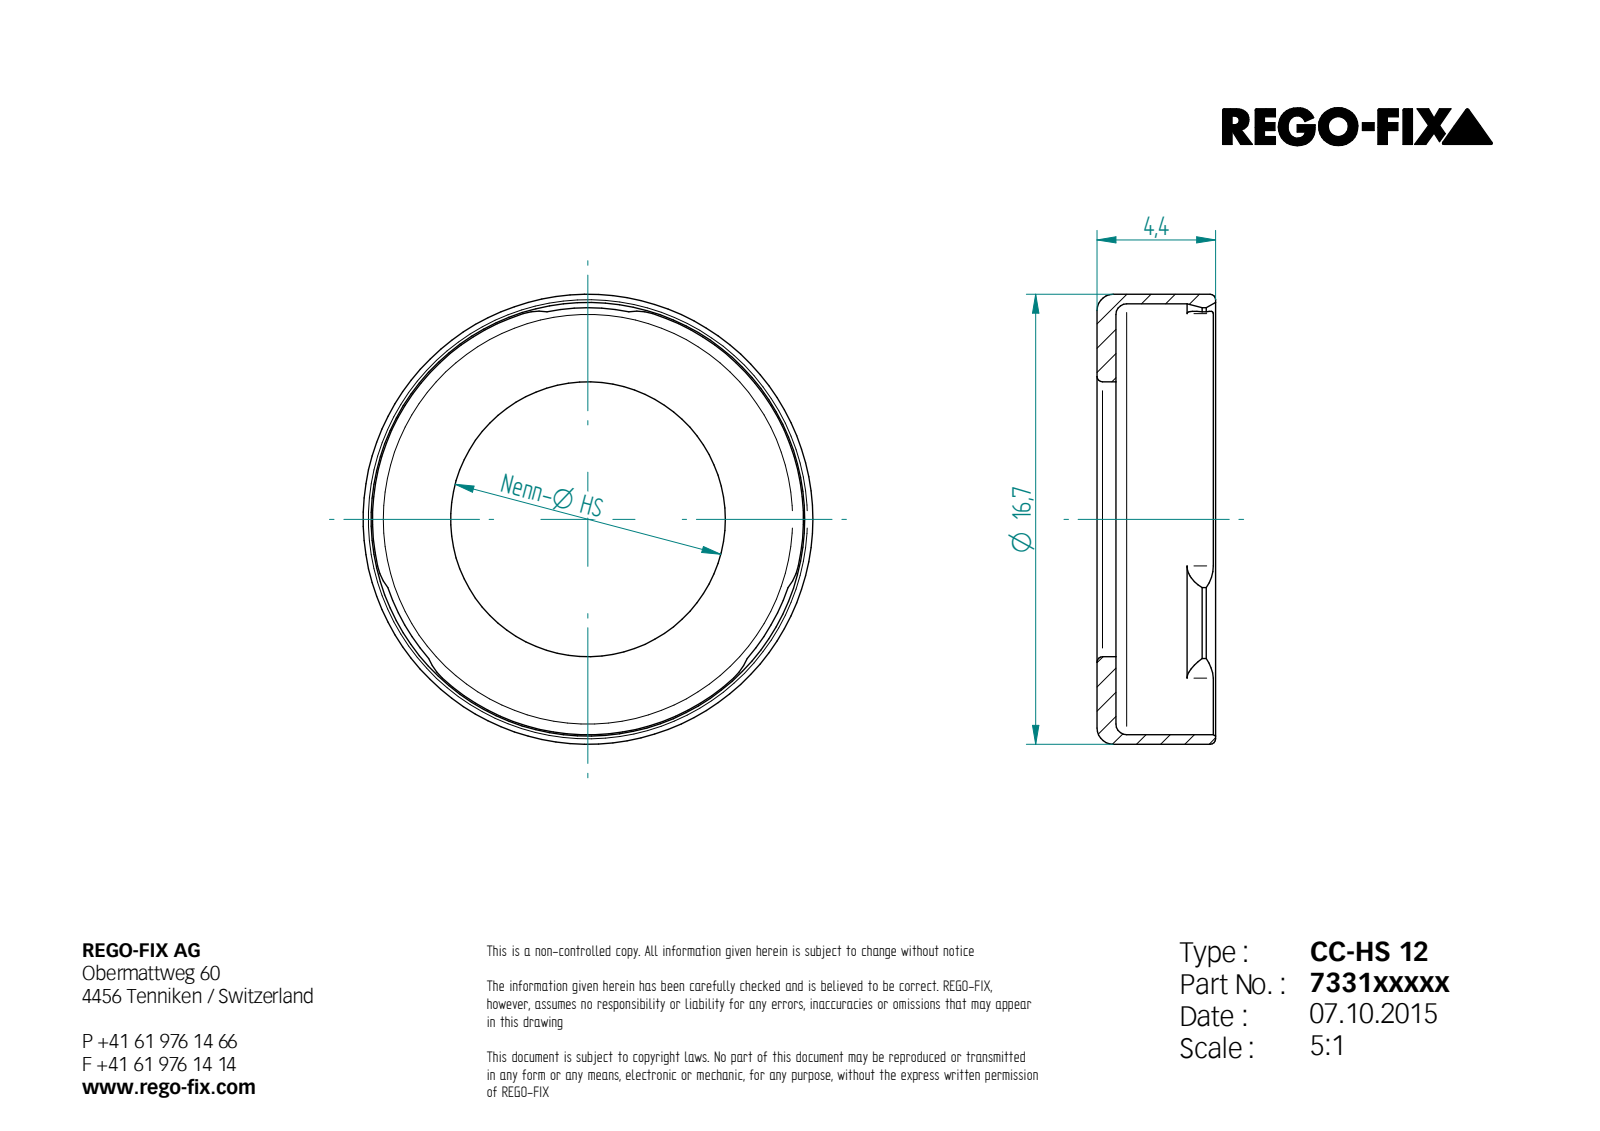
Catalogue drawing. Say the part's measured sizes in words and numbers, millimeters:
Its 3-D file was written by "Unknown (AUTOMOTIVE_DESIGN)". It is 1 solid with 23 faces: 3 planar, 12 cylindrical and 8 other. Overall it measures 16.7 by 16.7 by 4.4 millimeters. Its volume is 161 cubic millimeters and its surface area 683 square millimeters. Round holes: 1 of diameter 10.2, 1 of diameter 16. Round bosses or shafts: 1 of diameter 16.7. Partial cylindrical surfaces (rounded edges, fillets, slot ends): 6 of radius 2, 1 of radius 7.85. The main face-to-face distances are 0.7, 4.4, 3.7.
